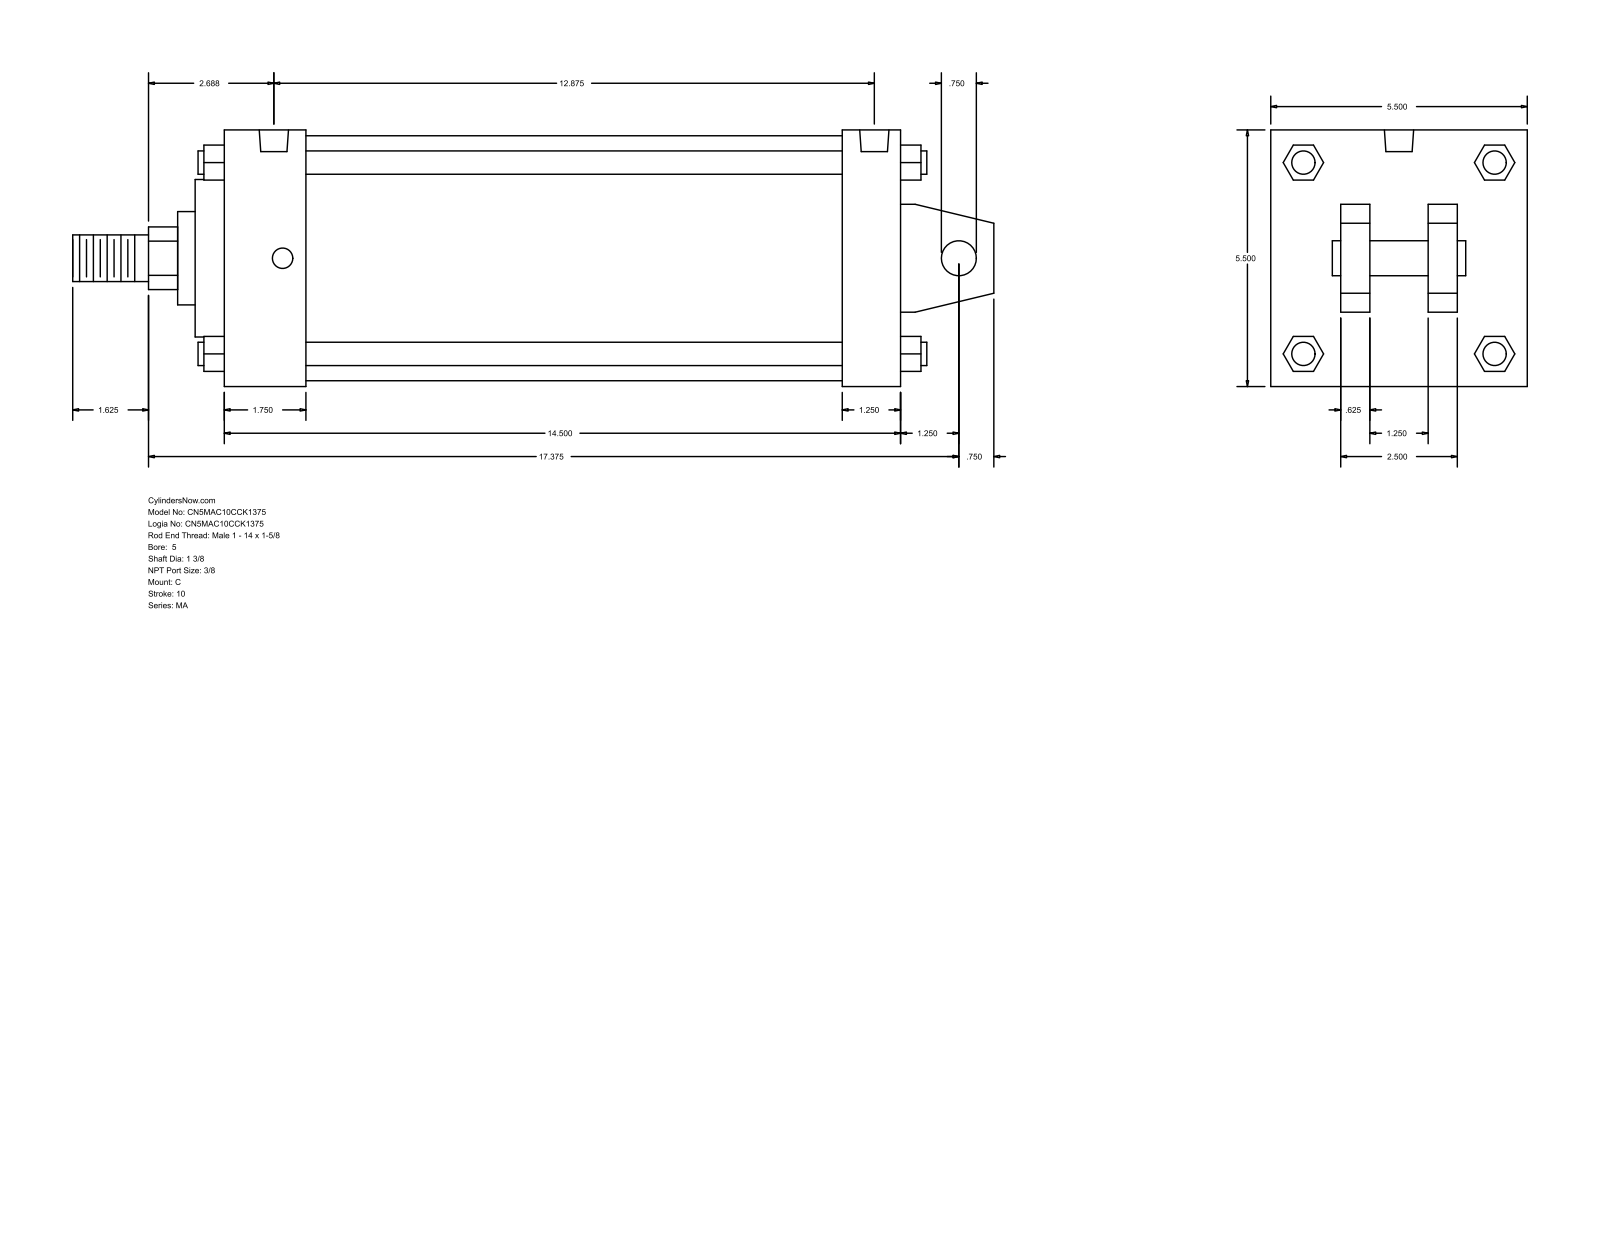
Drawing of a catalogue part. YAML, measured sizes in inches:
part_name: "MA_C__0500_1.375"
step_written_by: "GSSL Pune (CONFIG_CONTROL_DESIGN)"
units: inches
bodies: {solids: 0, faces: 141, planar: 109, cylindrical: 32, other: 0}
overall_size: [19.75, 5.5, 5.5]
round_holes:
  - {diameter: 0.437, count: 4}
  - {diameter: 0.627, count: 2}
round_bosses_or_shafts:
  - {diameter: 0.5, count: 4}
  - {diameter: 5.25, count: 1}
  - {diameter: 3.375, count: 1}
  - {diameter: 2, count: 1}
  - {diameter: 1.375, count: 1}
  - {diameter: 1, count: 1}
  - {diameter: 0.75, count: 1}
partial_cylinders:
  - {radius: 0.672, count: 1}
face_to_face_distances: [5.5, 14.5, 0.625, 13.25, 1.25, 1.75, 11.5, 12.75, 2.125, 1.5]
hole_center_spacings: [0.188, 12.5, 12.687, 12.875]
